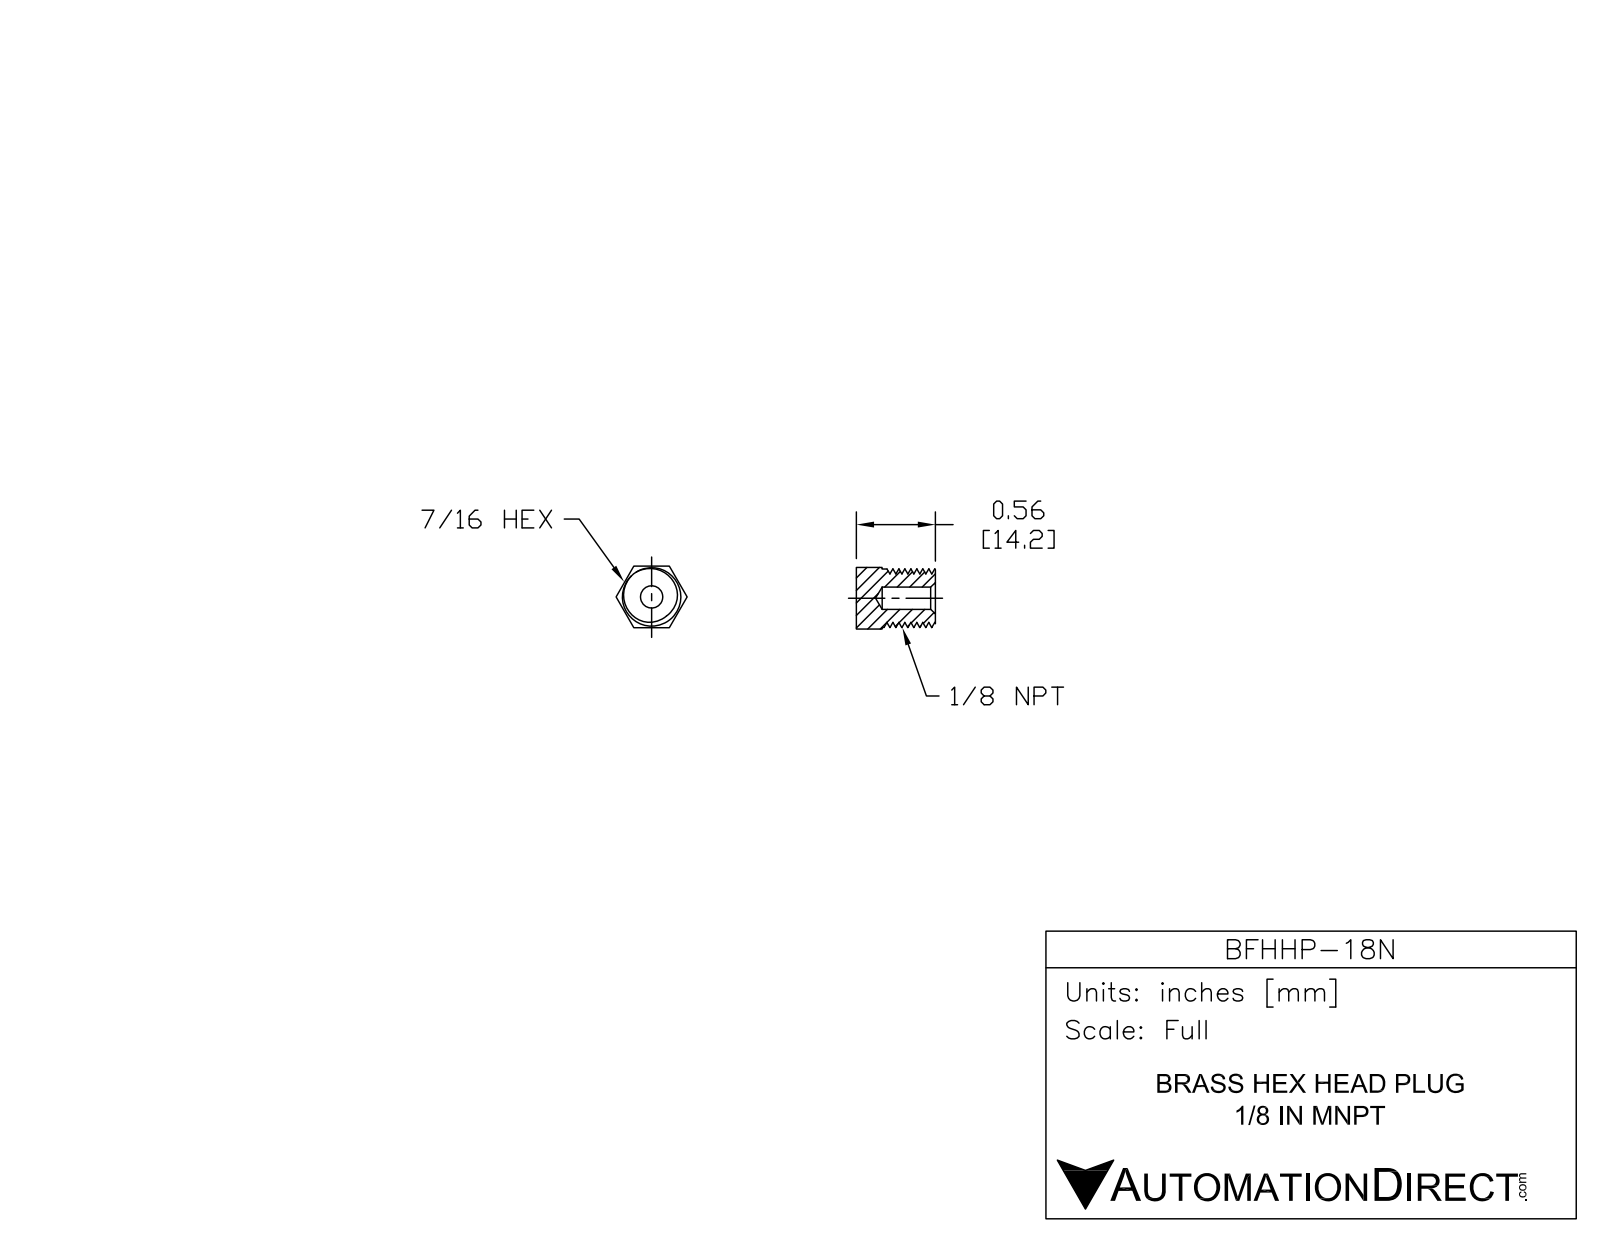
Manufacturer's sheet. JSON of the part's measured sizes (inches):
{"part_name": "BFHHP-18N", "step_written_by": "SolidWorks 2015 (CONFIG_CONTROL_DESIGN)", "units": "inches", "bodies": {"solids": 1, "faces": 36, "planar": 10, "cylindrical": 21, "other": 5}, "overall_size": [0.555, 0.508, 0.44], "volume_in3": 0.063, "surface_area_in2": 1.637, "round_holes": [[0.156, 1]], "round_bosses_or_shafts": [[0.405, 1]], "face_to_face_distances": [0.44, 0.555, 0.18, 0.375]}
